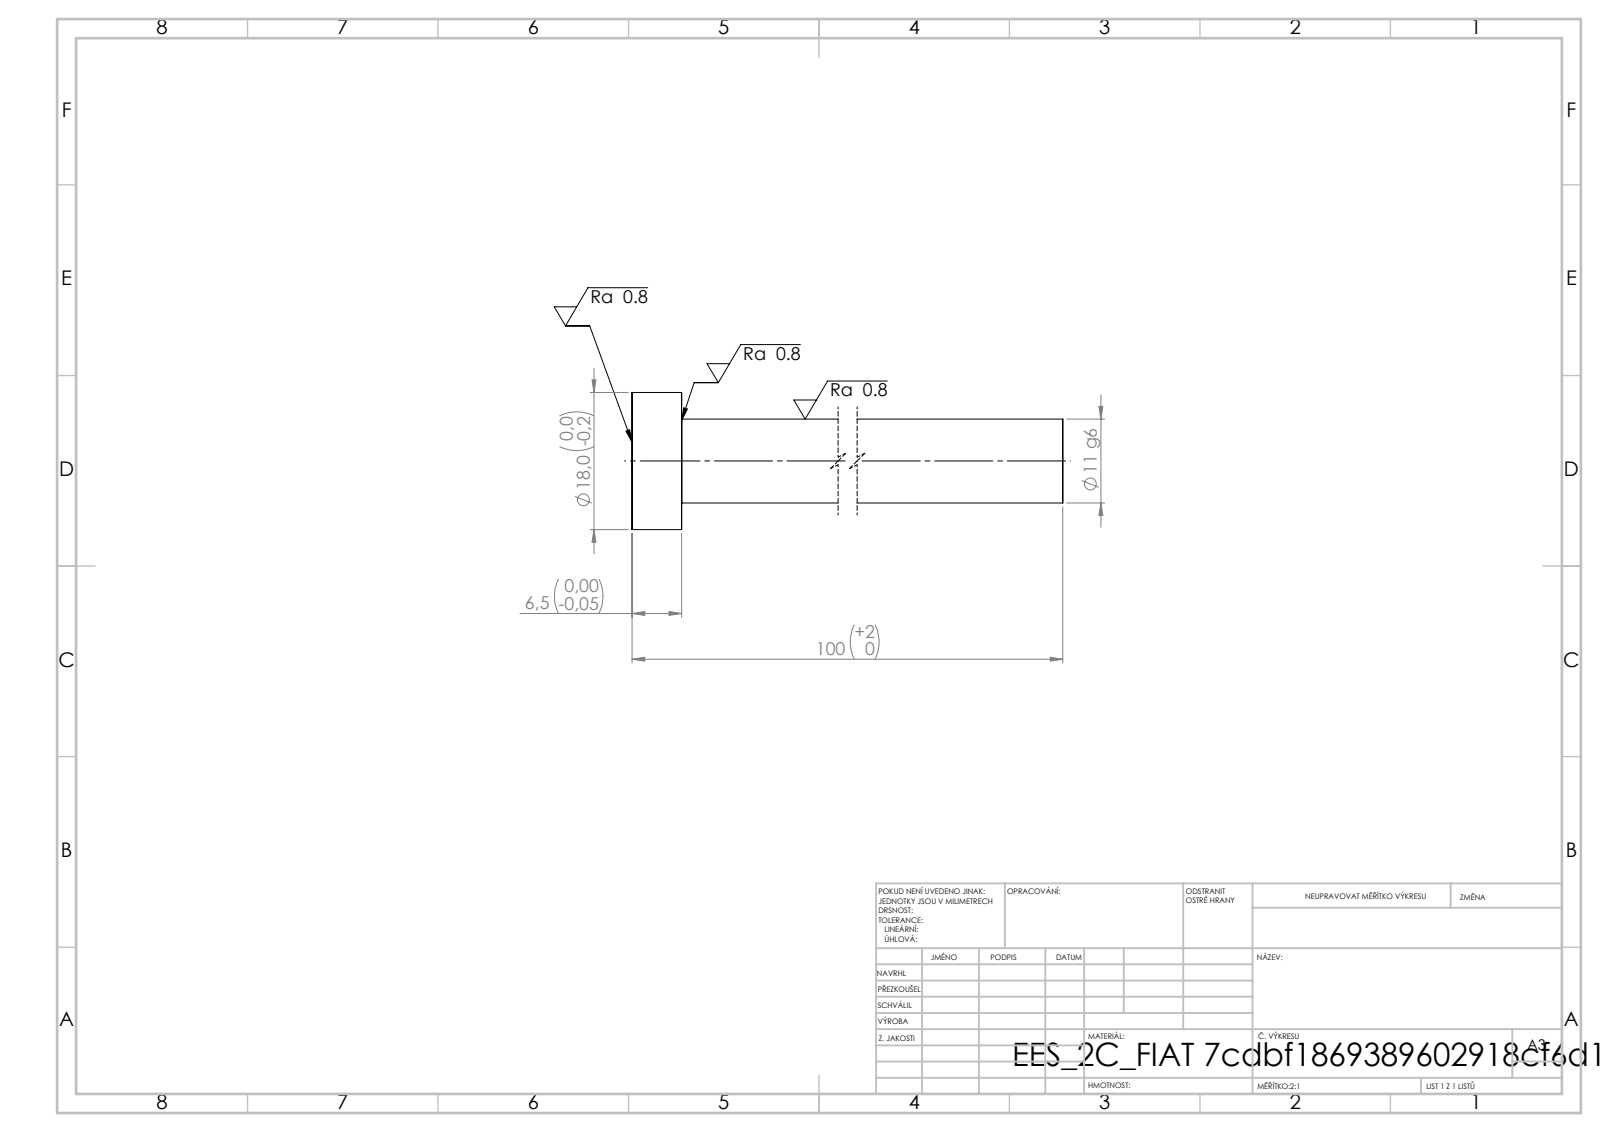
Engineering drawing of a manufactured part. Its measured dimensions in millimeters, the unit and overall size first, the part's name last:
Units: millimetres
Overall size (bounding box): 100 × 18 × 18
Round bosses / shafts (diameter × count): ⌀18 ×1, ⌀11 ×1
Main face-to-face distances: 6.5, 100, 93.5
Volume: 10 540 mm³ · Surface area: 4 108 mm²
Bodies: 1 solid, 7 faces (3 planar, 4 cylindrical, 0 other)
STEP written by: SolidWorks 2019 (CONFIG_CONTROL_DESIGN)
